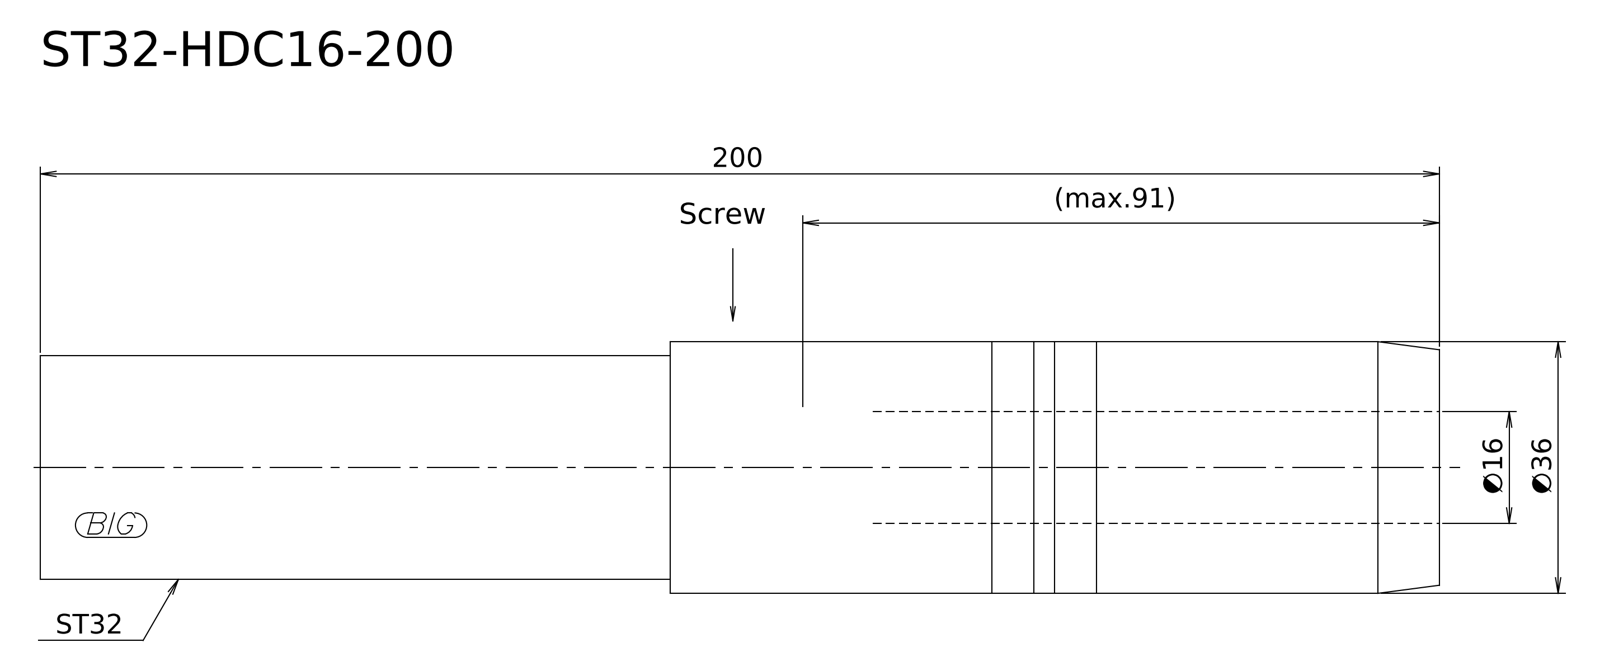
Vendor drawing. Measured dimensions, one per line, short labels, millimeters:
written by: Kubotek KeyCreator V8.5.1 (14335) (CONFIG_CONTROL_DESIGN)
unit: mm
bodies: 1 solid, 6 faces (3 planar, 2 cylindrical, 1 other)
size: 200 × 36 × 36
volume: 183 788 mm³; area: 23 374 mm²
bosses: 1× ⌀36, 1× ⌀32
face distances: 200, 110, 90
